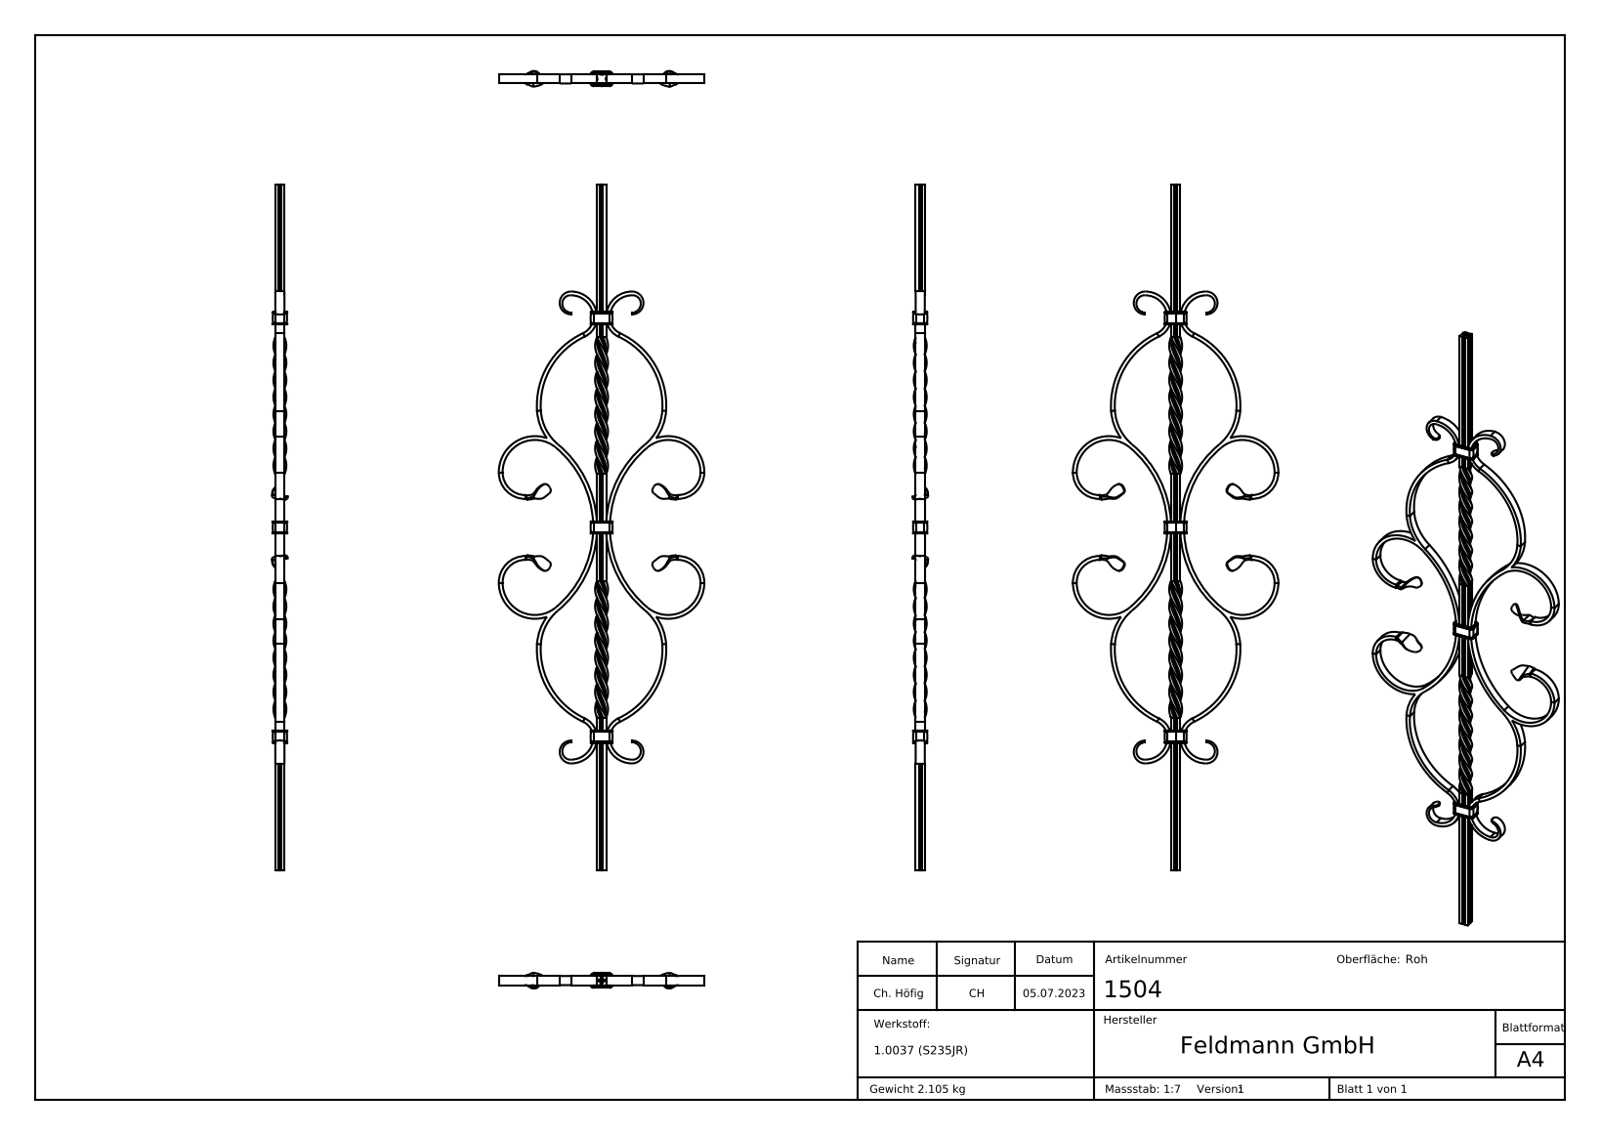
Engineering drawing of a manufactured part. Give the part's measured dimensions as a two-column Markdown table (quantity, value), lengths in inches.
| quantity | value |
| --- | --- |
| part name | 1504 |
| STEP written by | SolidWorks 2018 (CONFIG_CONTROL_DESIGN) |
| units | inches |
| bodies | 3 solids, 890 faces (362 planar, 235 cylindrical, 293 other) |
| overall size | 35.433 × 10.63 × 0.808 |
| volume | 16.47 in³ |
| surface area | 209.6 in² |
| partial cylindrical surfaces (radius × count) | 0.02 × 68, 0.008 × 24, 0.851 × 12, 0.039 × 4, 0.157 × 4, 0.197 × 4, 0.899 × 4, 1.096 × 4 |
| main face-to-face distances | 0.472, 0.352, 0.492, 0.02, 0.512, 0.217, 0.689, 10.827, 0.63, 0.906 |
